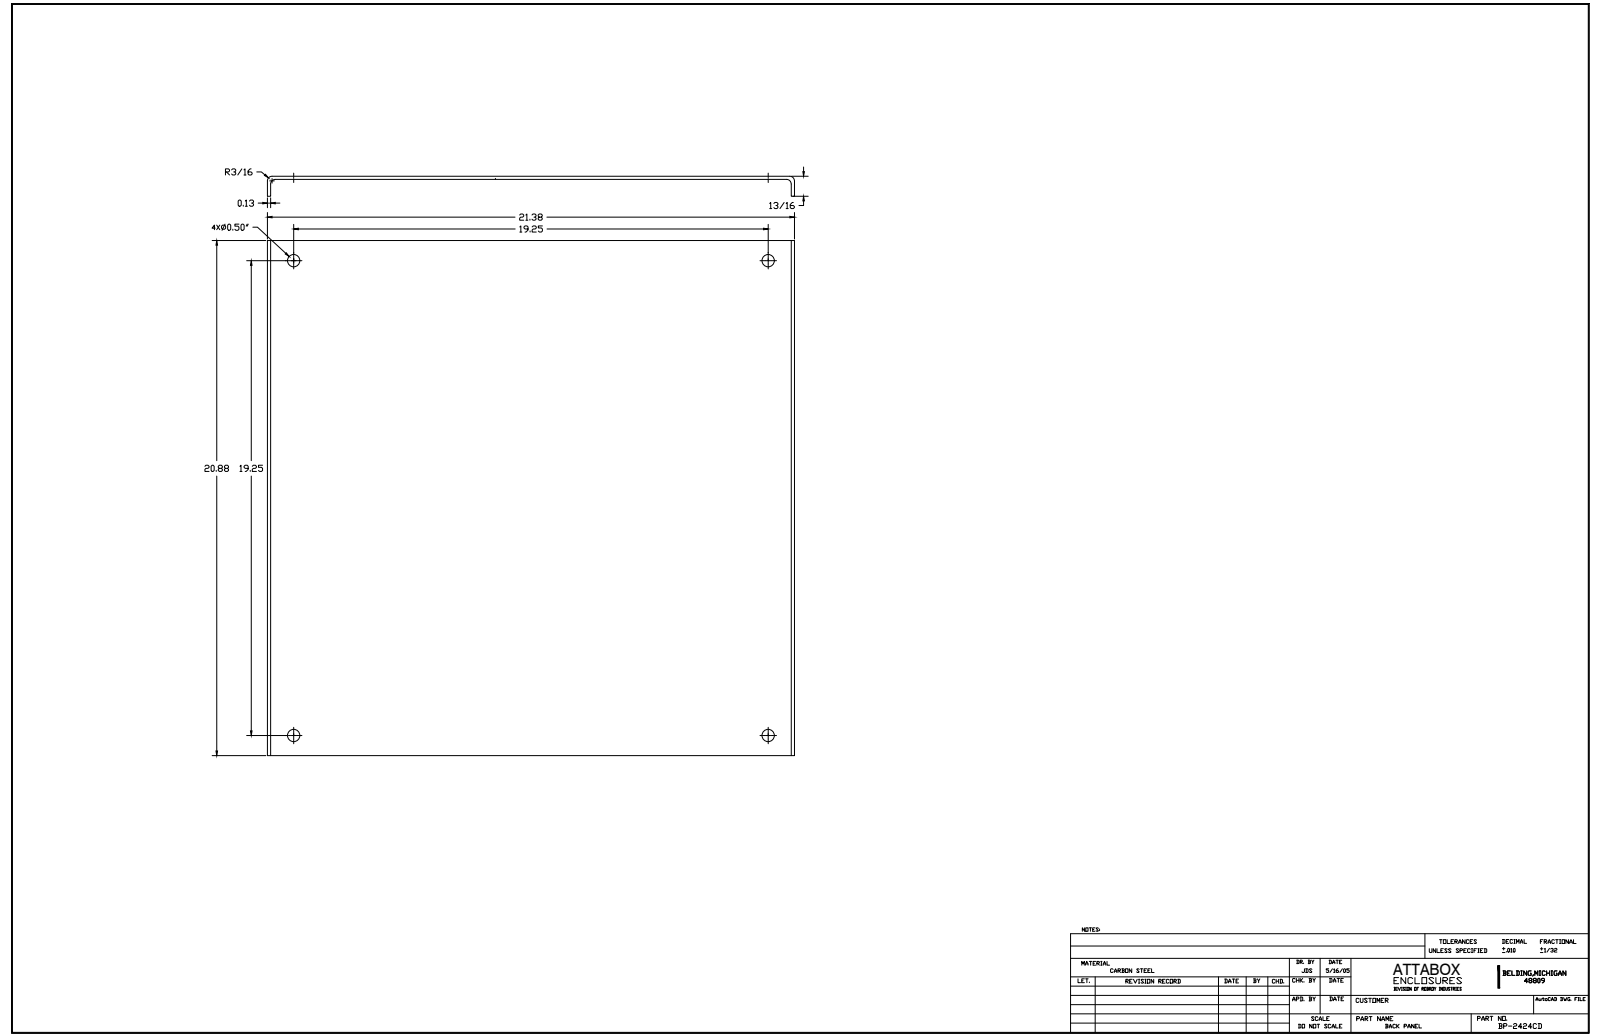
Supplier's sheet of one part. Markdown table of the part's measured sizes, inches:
| quantity | value |
| --- | --- |
| part name | BP2424CD |
| STEP written by | SolidWorks 2018 (AUTOMOTIVE_DESIGN) |
| units | inches |
| bodies | 1 solid, 18 faces (10 planar, 8 cylindrical, 0 other) |
| overall size | 21.375 × 20.875 × 0.5 |
| volume | 59.63 in³ |
| surface area | 929.2 in² |
| round holes (diameter × count) | 0.5 × 4 |
| partial cylindrical surfaces (radius × count) | 0.063 × 2, 0.188 × 2 |
| main face-to-face distances | 0.13, 21.245, 21.375, 21.115, 0.37, 0.5, 20.875 |
| hole center spacings | 19.25, 19.25, 27.224, 27.224 |
